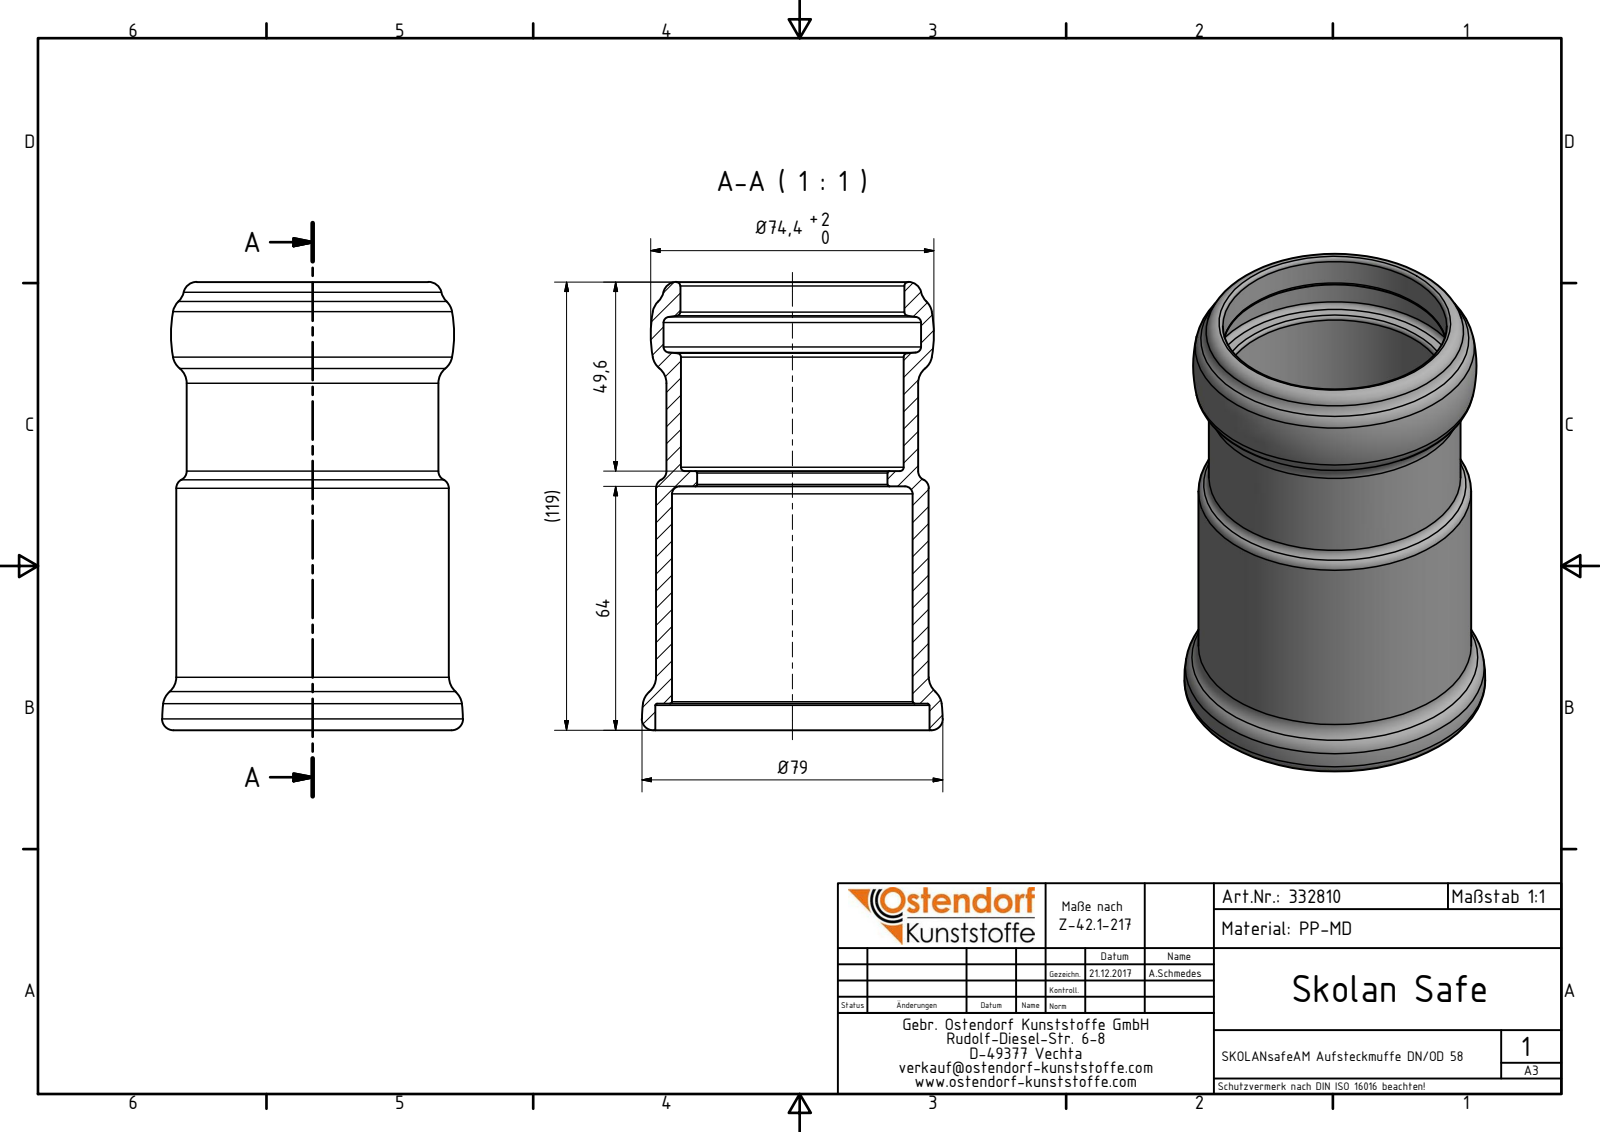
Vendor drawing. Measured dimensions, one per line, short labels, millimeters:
name: 332810 SKOLANsafeAM Aufsteckmuffe DN_OD 58
written by: Autodesk Inventor 2016 (AUTOMOTIVE_DESIGN)
unit: mm
bodies: 1 solid, 37 faces (4 planar, 8 cylindrical, 25 other)
size: 117.6 × 79 × 79
volume: 108 826 mm³; area: 54 758 mm²
holes: 1× ⌀50, 1× ⌀58.5, 1× ⌀58.8, 1× ⌀63.2, 1× ⌀67.6, 1× ⌀72
bosses: 1× ⌀71.6, 1× ⌀66.1
face distances: 57, 61, 4, 7, 64, 68
